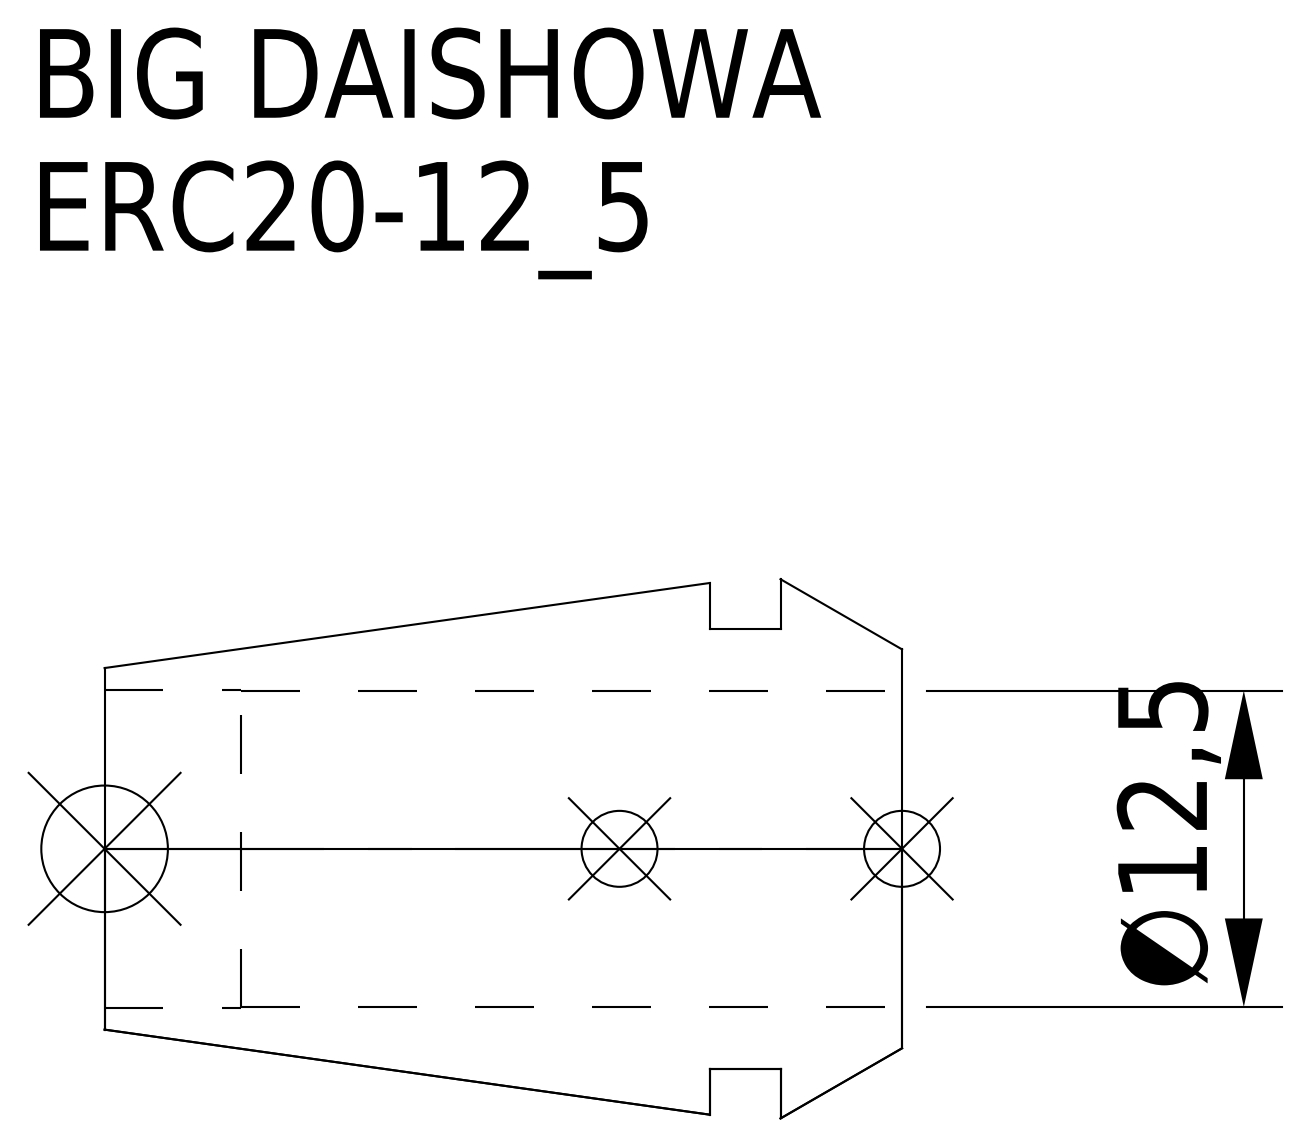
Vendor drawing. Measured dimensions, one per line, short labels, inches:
name: ERC20-12_5
written by: CREO PARAMETRIC BY PTC INC, 2016380 (AUTOMOTIVE_DESIGN)
unit: in
bodies: 1 solid, 15 faces (5 planar, 6 cylindrical, 4 other)
size: 1.24 × 0.839 × 0.839
volume: 0.245 in³; area: 5.251 in²
holes: 1× ⌀0.492, 1× ⌀0.494
bosses: 1× ⌀0.685
face distances: 0.11, 0.189, 0.299, 1.24, 1.051, 0.941, 1.028, 0.839, 0.728, 0.213
